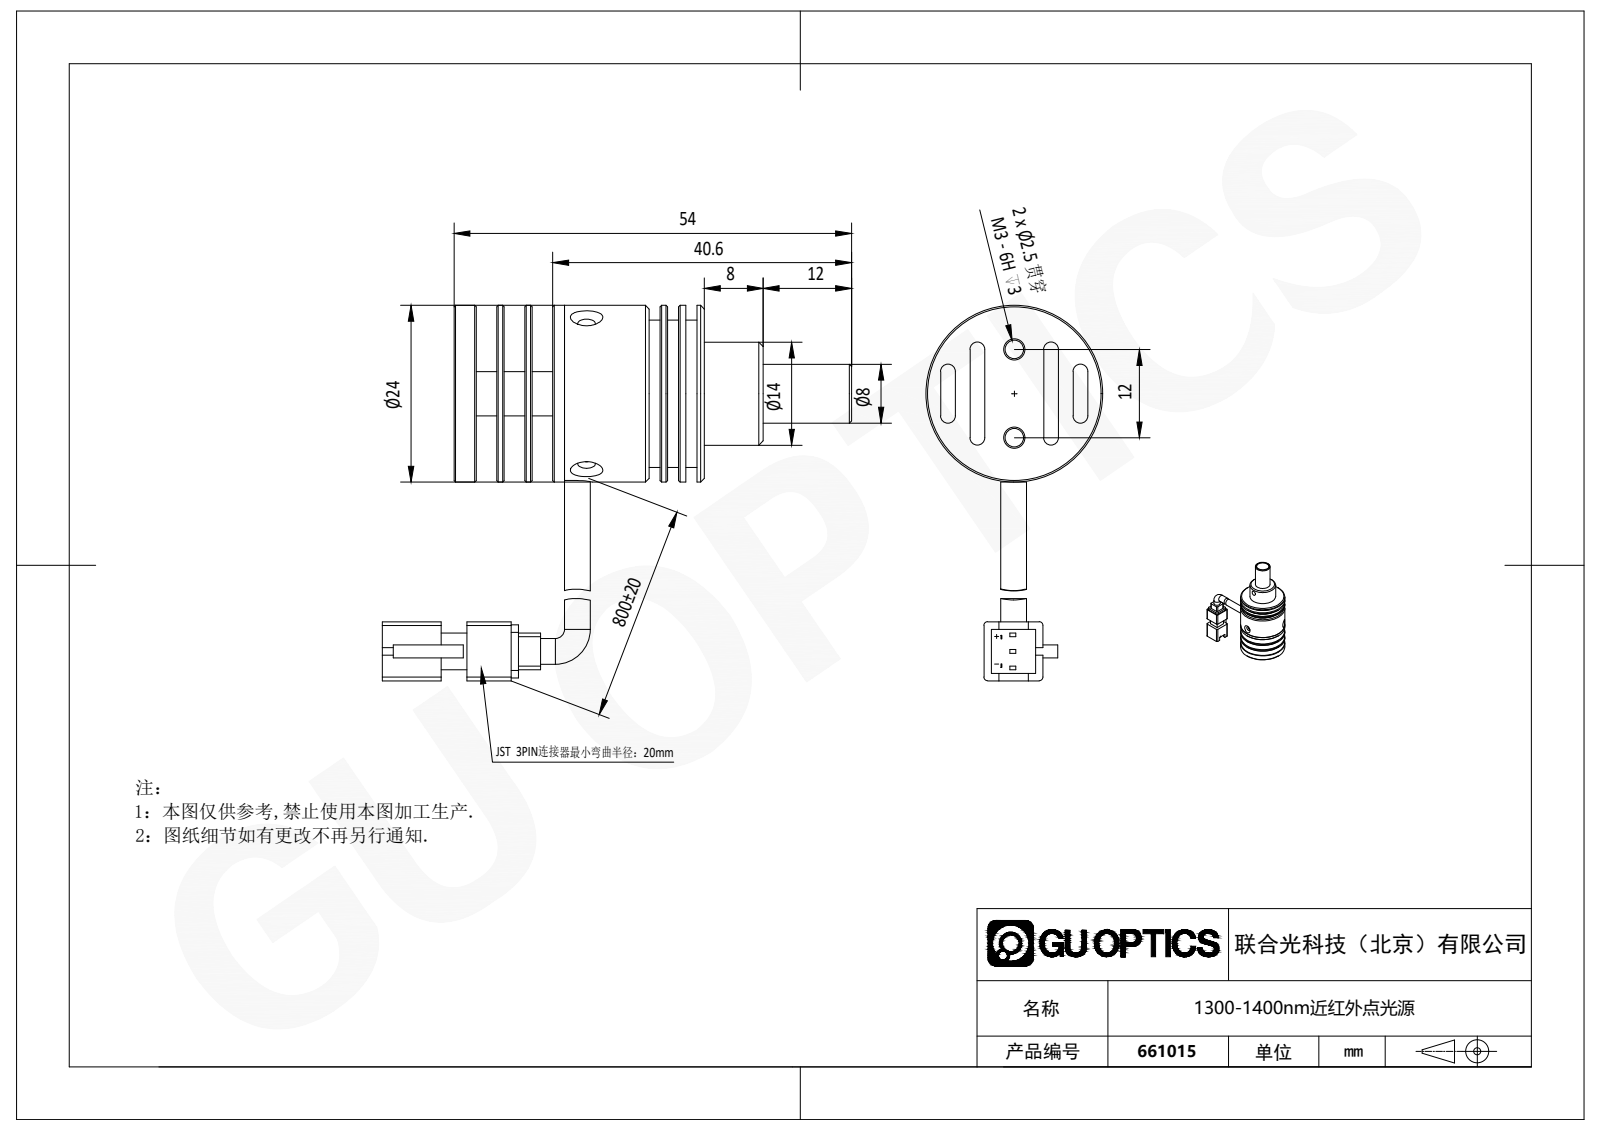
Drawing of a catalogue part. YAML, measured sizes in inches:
part_name: "661012"
step_written_by: "SolidWorks 2020 (AUTOMOTIVE_DESIGN)"
units: inches
bodies: {solids: 10, faces: 387, planar: 153, cylindrical: 160, other: 74}
overall_size: [2.51, 2.008, 0.945]
volume: 0.692
surface_area: 21.4
round_holes:
  - {diameter: 0.063, count: 7}
  - {diameter: 0.079, count: 3}
  - {diameter: 0.094, count: 3}
  - {diameter: 0.098, count: 3}
  - {diameter: 0.087, count: 2}
  - {diameter: 0.244, count: 1}
  - {diameter: 0.268, count: 1}
  - {diameter: 0.472, count: 1}
  - {diameter: 0.622, count: 1}
  - {diameter: 0.661, count: 1}
  - {diameter: 0.752, count: 1}
  - {diameter: 0.791, count: 1}
round_bosses_or_shafts:
  - {diameter: 0.138, count: 2}
  - {diameter: 0.945, count: 1}
  - {diameter: 0.787, count: 1}
  - {diameter: 0.669, count: 1}
  - {diameter: 0.614, count: 1}
  - {diameter: 0.567, count: 1}
  - {diameter: 0.551, count: 1}
  - {diameter: 0.543, count: 1}
partial_cylinders:
  - {radius: 0.039, count: 12}
  - {radius: 0.02, count: 8}
  - {radius: 0.059, count: 3}
  - {radius: 0.065, count: 1}
face_to_face_distances: [0.15, 0.039, 0.26, 0.11, 0.059, 0.299, 0.197, 0.409, 0.256, 0.098]
hole_center_spacings: [0.236, 0.334, 0.181, 0.181, 0.437, 0.473, 0.237, 0.436]
